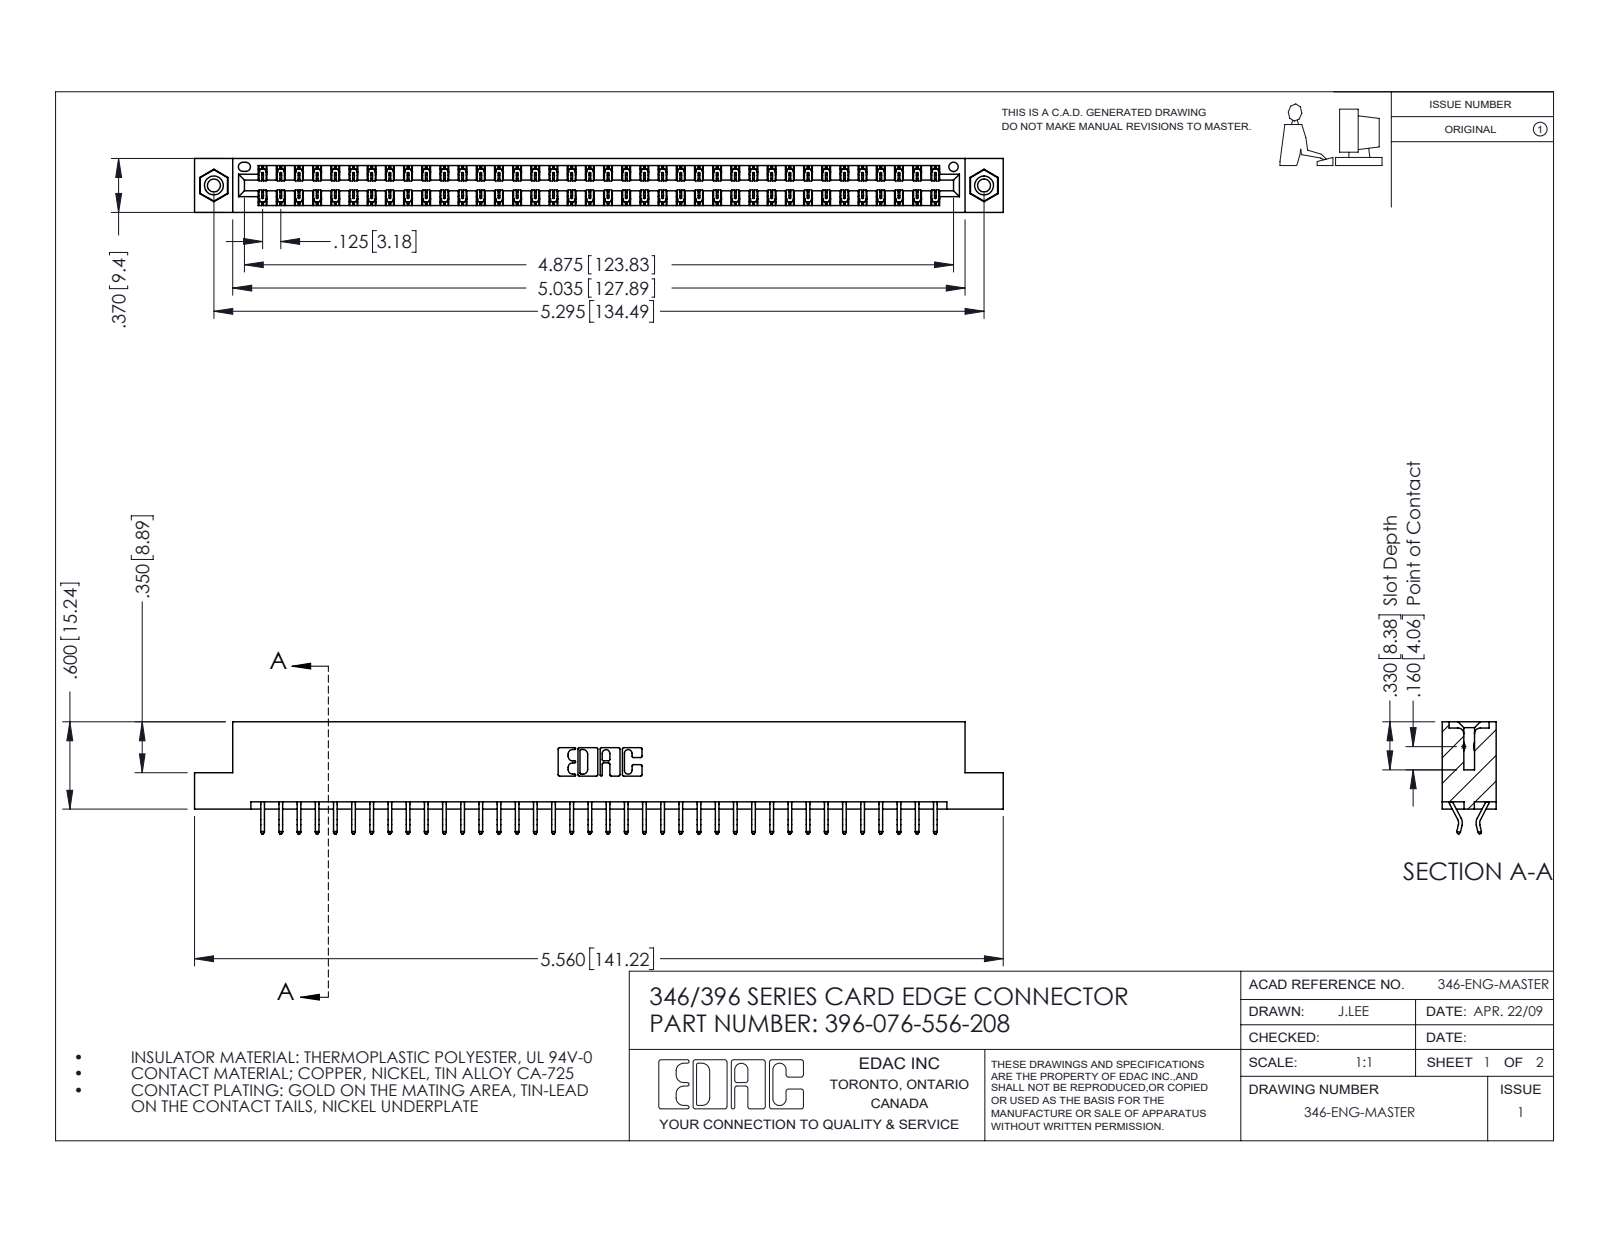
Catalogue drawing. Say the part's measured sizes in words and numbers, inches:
The part is named "345-292-001_556 Tail; 345-250-001_345-250-003-102; 396-076-556-208; 346 Part_Flush Mounting Lugs - 0.156 Dia-TI". Its 3-D file was written by "SolidWorks 2016 (CONFIG_CONTROL_DESIGN)". It is 79 solids with 4590 faces: 3072 planar, 1502 cylindrical and 16 other. Overall it measures 5.56 by 0.77 by 0.37 inches. Its volume is 0.838 cubic inches and its surface area 29.08 square inches. Round holes: 2 of diameter 0.089, 2 of diameter 0.125, 2 of diameter 0.156, 1 of diameter 0.064. Round bosses or shafts: 2 of diameter 0.155. Partial cylindrical surfaces (rounded edges, fillets, slot ends): 114 of radius 0.006, 22 of radius 0.01, 6 of radius 0.007, 6 of radius 0.031, 3 of radius 0.026, 2 of radius 0.01, 2 of radius 0.014, 2 of radius 0.022. The main face-to-face distances are 0.048, 0.322, 0.37, 0.25, 0.025, 0.072, 0.298, 0.275, 0.148, 0.222. The hole center spacings are 0.246, 5.086, 5.295.
